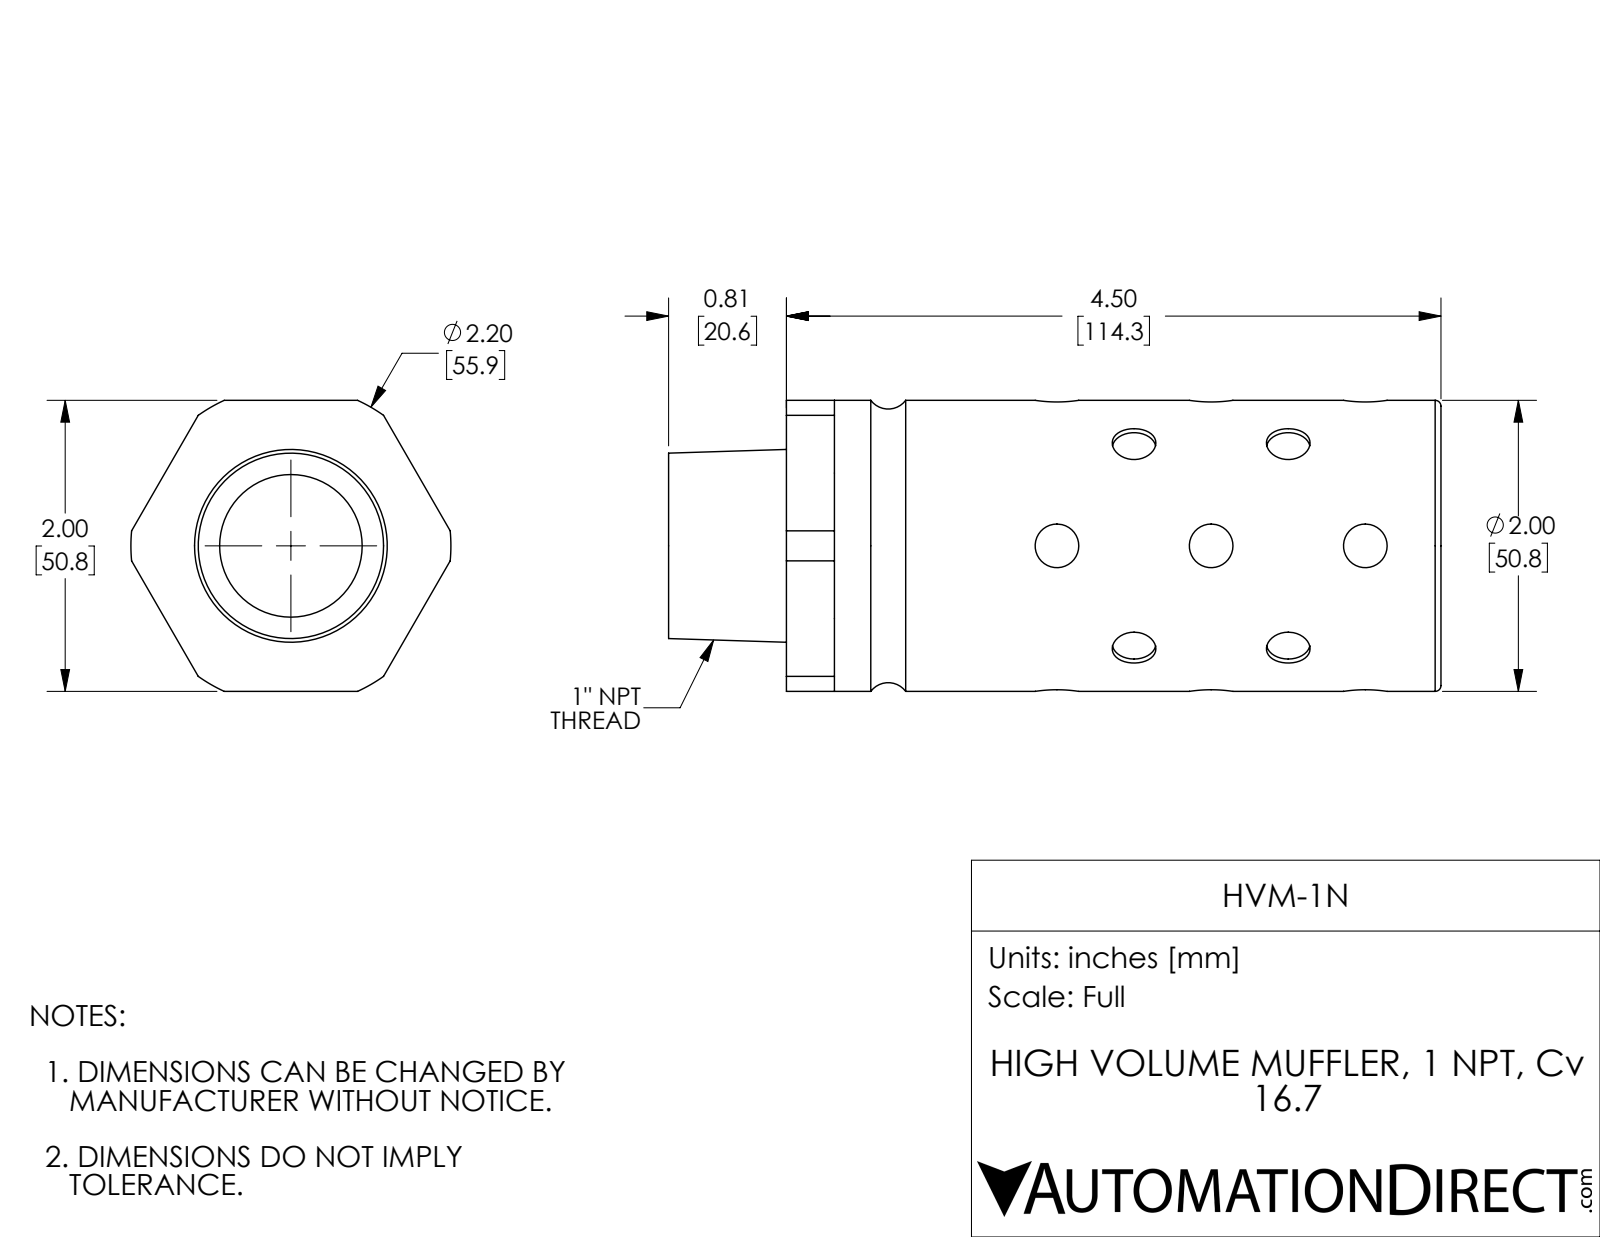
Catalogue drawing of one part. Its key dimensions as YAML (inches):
part_name: "HVM-1N"
step_written_by: "SolidWorks 2017 (AUTOMOTIVE_DESIGN)"
units: inches
bodies: {solids: 1, faces: 97, planar: 36, cylindrical: 53, other: 8}
overall_size: [5.31, 2.2, 2]
volume: 11.36
surface_area: 54.96
round_holes:
  - {diameter: 0.3, count: 14}
  - {diameter: 0.98, count: 1}
round_bosses_or_shafts:
  - {diameter: 2, count: 1}
partial_cylinders:
  - {radius: 1.1, count: 1}
face_to_face_distances: [4.5, 2, 4.25, 0.25, 1.9, 0.81, 5.06, 5.31, 0.05, 1.95]
hole_center_spacings: [1.06, 1.06, 2.12]
